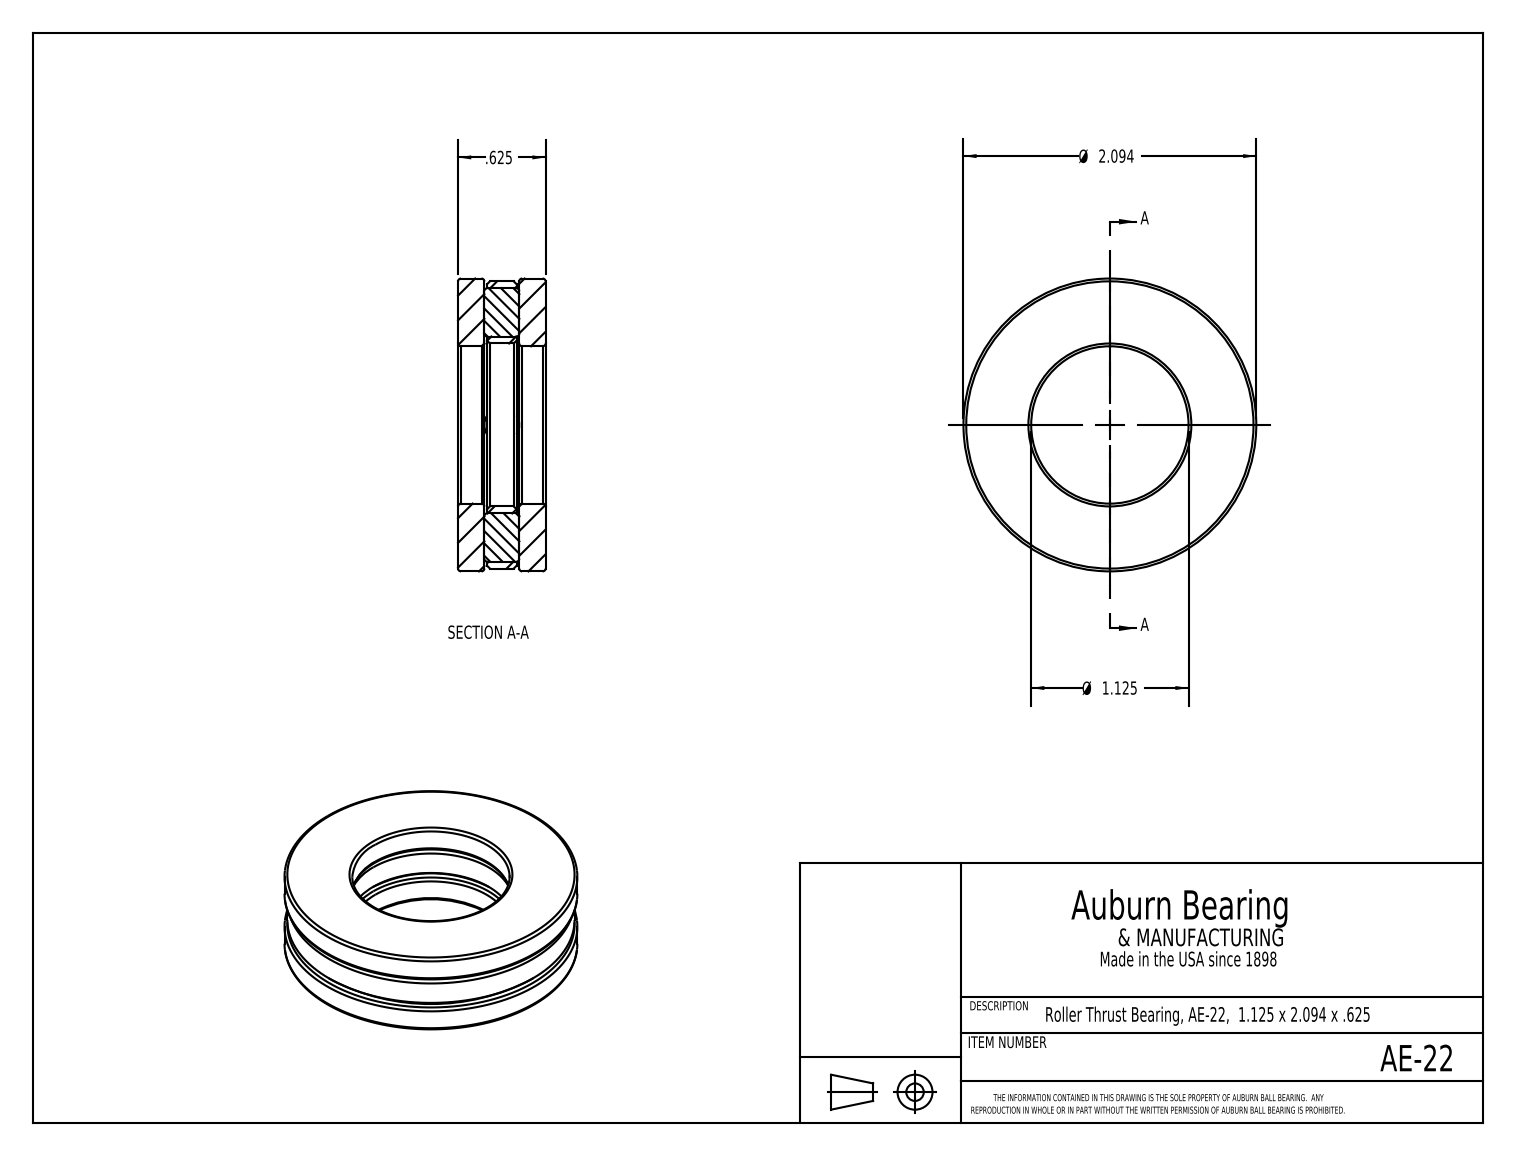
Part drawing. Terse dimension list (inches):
name: AE-22
written by: SolidWorks 2017 (CONFIG_CONTROL_DESIGN)
unit: in
bodies: 7 solids, 60 faces (30 planar, 10 cylindrical, 20 other)
size: 2.094 × 2.094 × 0.625
volume: 1.377 in³; area: 21.35 in²
holes: 1× ⌀1.125, 1× ⌀1.165
bosses: 2× ⌀0.25, 1× ⌀2.094, 1× ⌀2.054
face distances: 0.207, 0.418, 0.25, 0.187, 0.437, 0.625, 0.438, 0.188, 0.02, 0.23
